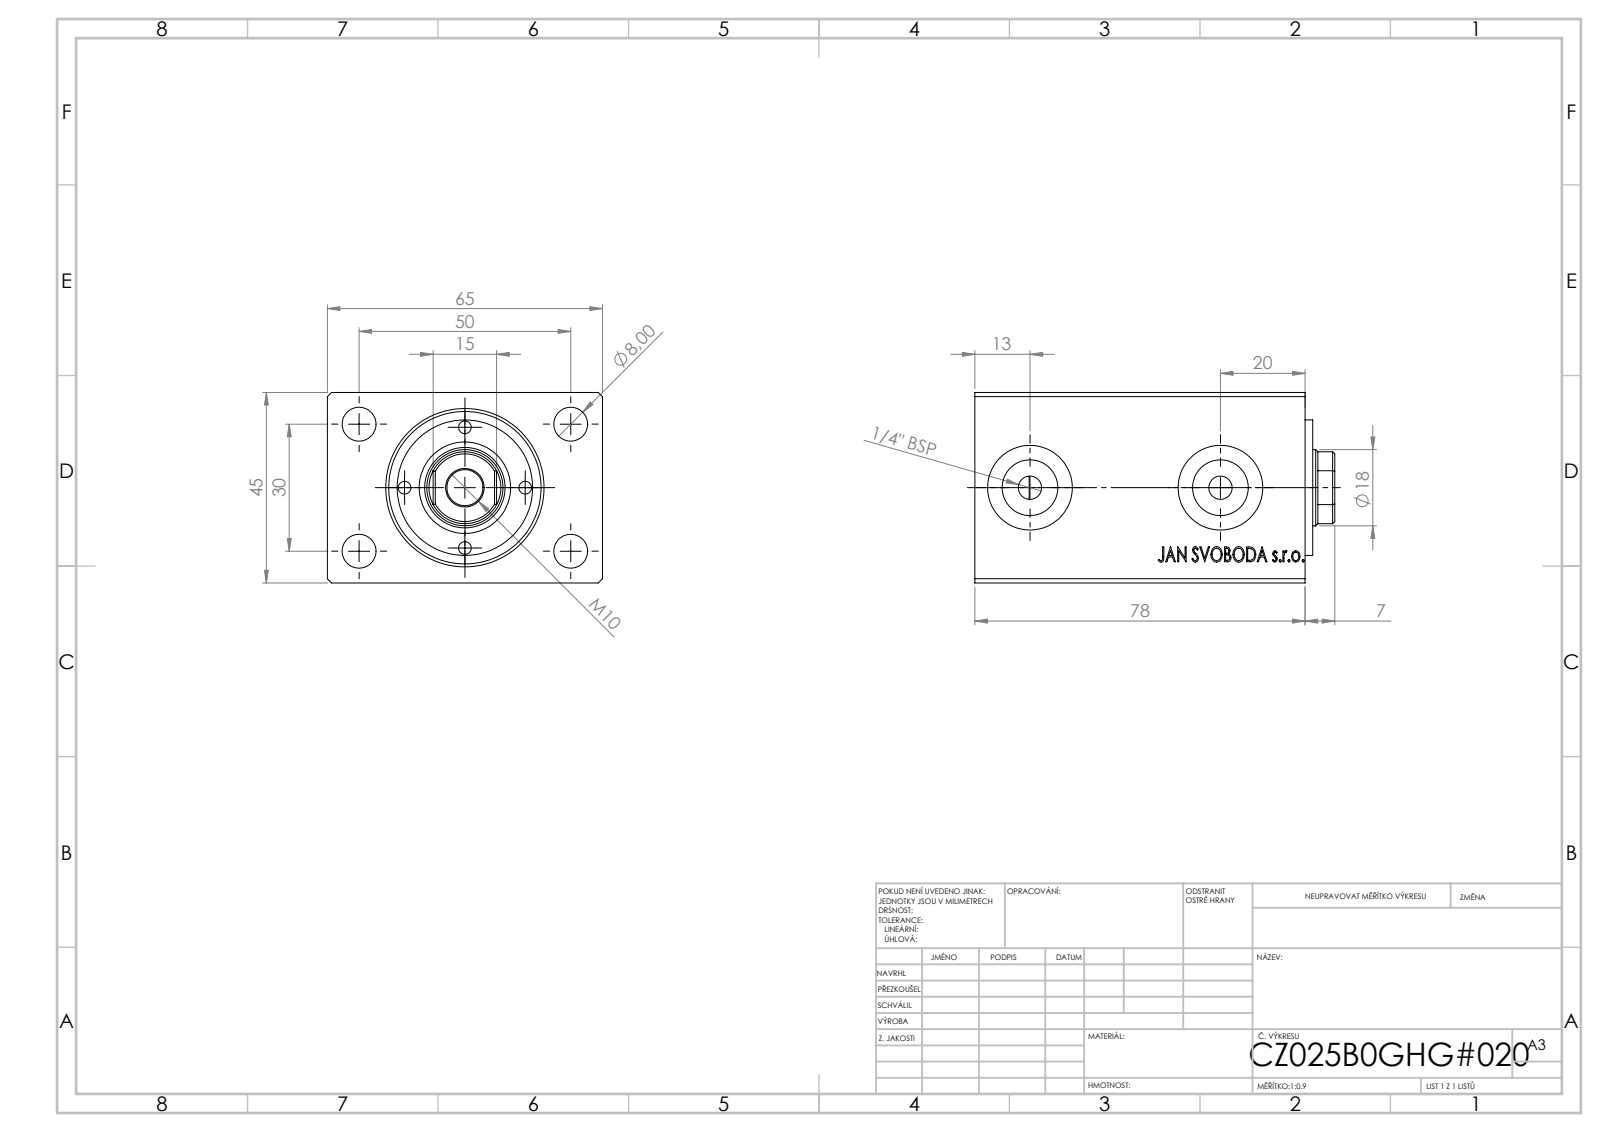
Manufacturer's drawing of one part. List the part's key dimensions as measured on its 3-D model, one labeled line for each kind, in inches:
Part name (STEP PRODUCT): V500CZ_B_VC; V500CZ
STEP written by: SolidWorks 2019 (CONFIG_CONTROL_DESIGN)
Units: inches
Bodies: 3 solids, 873 faces (399 planar, 58 cylindrical, 416 other)
Overall size (bounding box): 3.346 × 2.559 × 1.772
Volume: 13.36 in³ · Surface area: 83.72 in²
Round holes (diameter × count): ⌀0.118 ×4, ⌀0.315 ×4, ⌀0.217 ×2, ⌀0.518 ×2, ⌀0.787 ×2, ⌀0.335 ×1, ⌀0.709 ×1, ⌀0.748 ×1, ⌀0.984 ×1, ⌀1.417 ×1
Round bosses / shafts (diameter × count): ⌀1.26 ×1
Partial cylindrical surfaces — rounded edges, fillets, slot ends (radius × count): R0.335 ×1
Main face-to-face distances: 1.772, 2.559, 3.071, 0.787, 2.283, 3.063, 0.78, 0.335, 0.445, 2.618
Hole centre spacings: 0.561, 0.726, 0.793, 0.985, 1.148, 1.515, 1.654, 1.122
